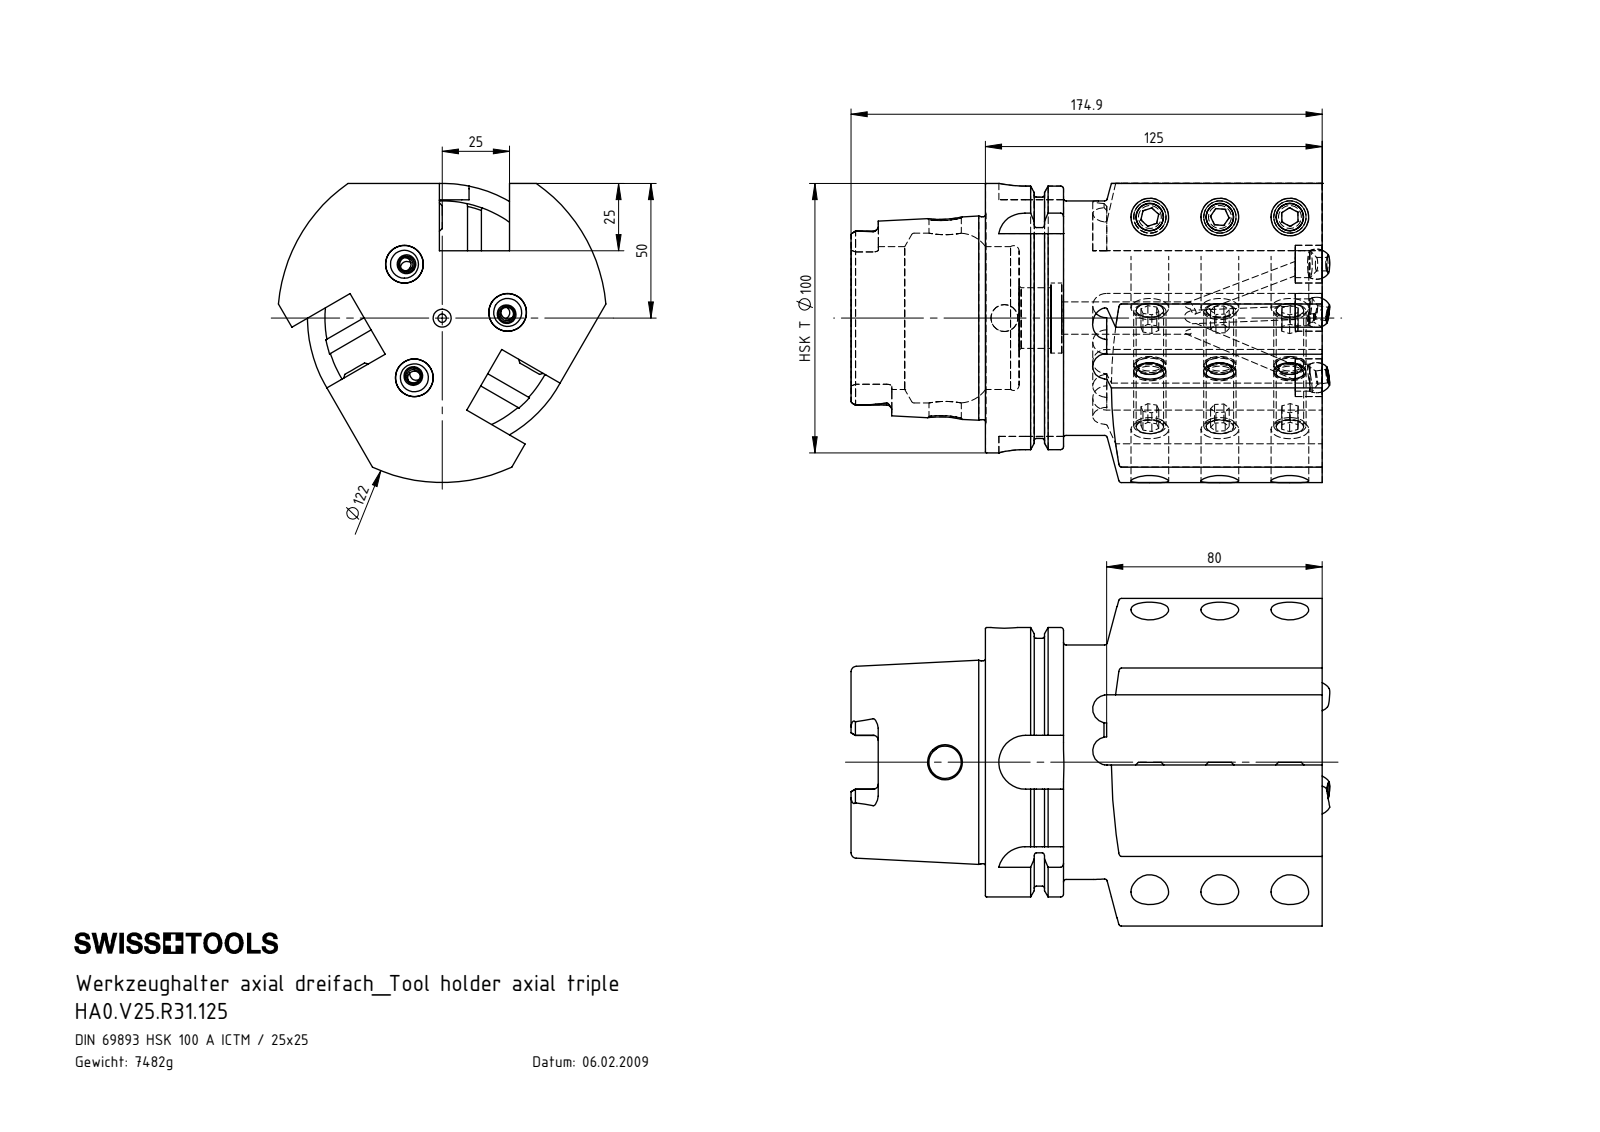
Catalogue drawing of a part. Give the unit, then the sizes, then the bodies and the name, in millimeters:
Units: millimetres
Overall size (bounding box): 177.71 × 121.55 × 111
Round holes (diameter × count): ⌀14 ×12, ⌀10.2 ×9, ⌀5 ×6, ⌀10 ×4, ⌀12 ×2, ⌀3.15 ×1, ⌀22.5 ×1, ⌀26 ×1, ⌀53 ×1, ⌀63 ×1
Round bosses / shafts (diameter × count): ⌀12 ×9, ⌀100 ×1, ⌀91.95 ×1, ⌀87 ×1, ⌀75.26 ×1
Partial cylindrical surfaces — rounded edges, fillets, slot ends (radius × count): R1.9 ×6, R5.2 ×6, R4.88 ×4, R10 ×4, R61 ×1
Main face-to-face distances: 25, 26, 125, 12.45, 112.55, 28.95, 16.5, 96.05, 49.9, 62.35
Hole centre spacings: 26, 24.41, 52, 42.28, 42.29, 65.74, 88.35, 112.44
Volume: 954 645 mm³ · Surface area: 135 895 mm²
Bodies: 16 solids, 338 faces (149 planar, 84 cylindrical, 105 other)
Part name (STEP PRODUCT): HA0.V25.R31.125; KU1-U14.001.012_2; KU1-U14.001.012_1; KU1-U14.001.012 (+2 more)
STEP written by: SolidWorks 2017 (AUTOMOTIVE_DESIGN)
